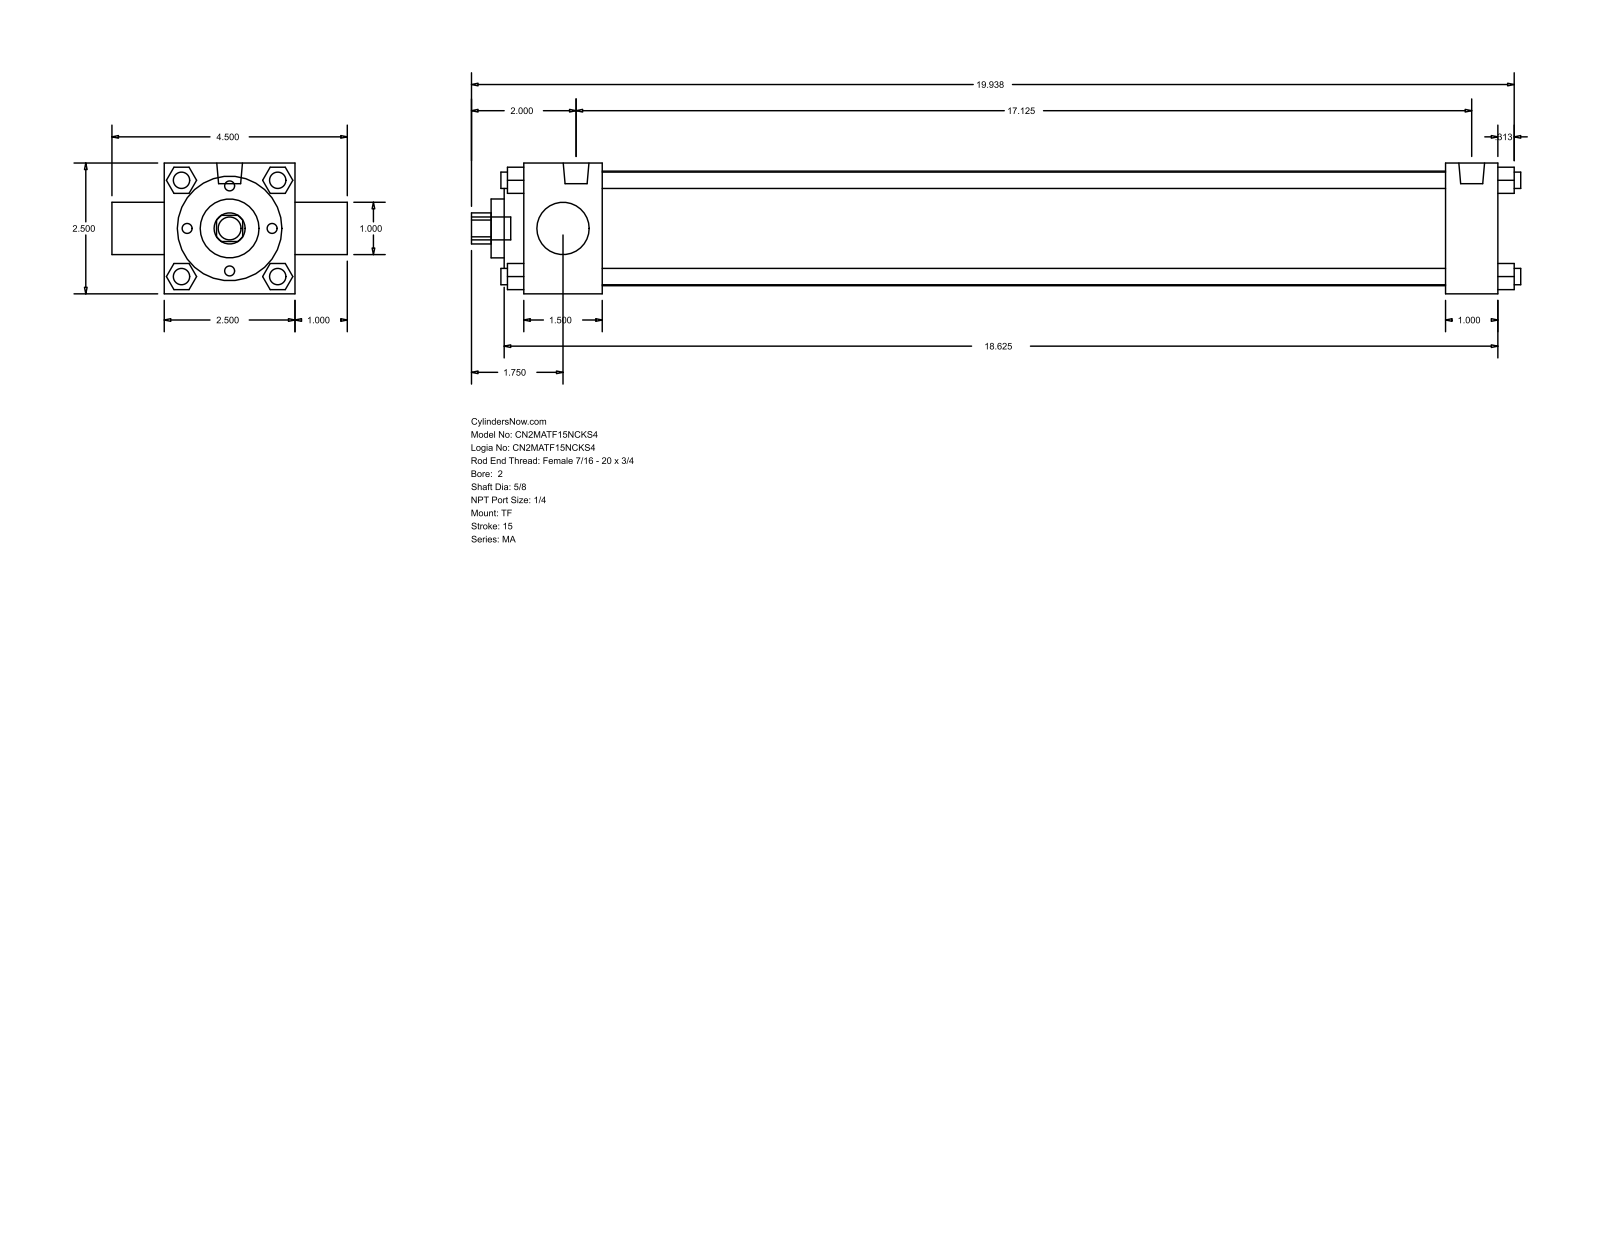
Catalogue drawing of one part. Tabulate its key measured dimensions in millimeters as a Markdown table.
| quantity | value |
| --- | --- |
| part name | MA_TF__0200_0.625 |
| STEP written by | GSSL Pune (CONFIG_CONTROL_DESIGN) |
| units | millimeters |
| bodies | 0 solids, 122 faces (93 planar, 29 cylindrical, 0 other) |
| overall size | 509.59 × 114.3 × 63.5 |
| round holes (diameter × count) | 15.88 × 1, 25.4 × 1, 28.57 × 1, 50.8 × 1, 55.63 × 1 |
| round bosses / shafts (diameter × count) | 7.94 × 7, 12.49 × 2, 11.11 × 1 |
| partial cylindrical surfaces (radius × count) | 7.54 × 1 |
| main face-to-face distances | 63.5, 38.1, 12.7, 9.52, 473.08, 447.67, 409.57, 434.98, 25.41, 47.62 |
